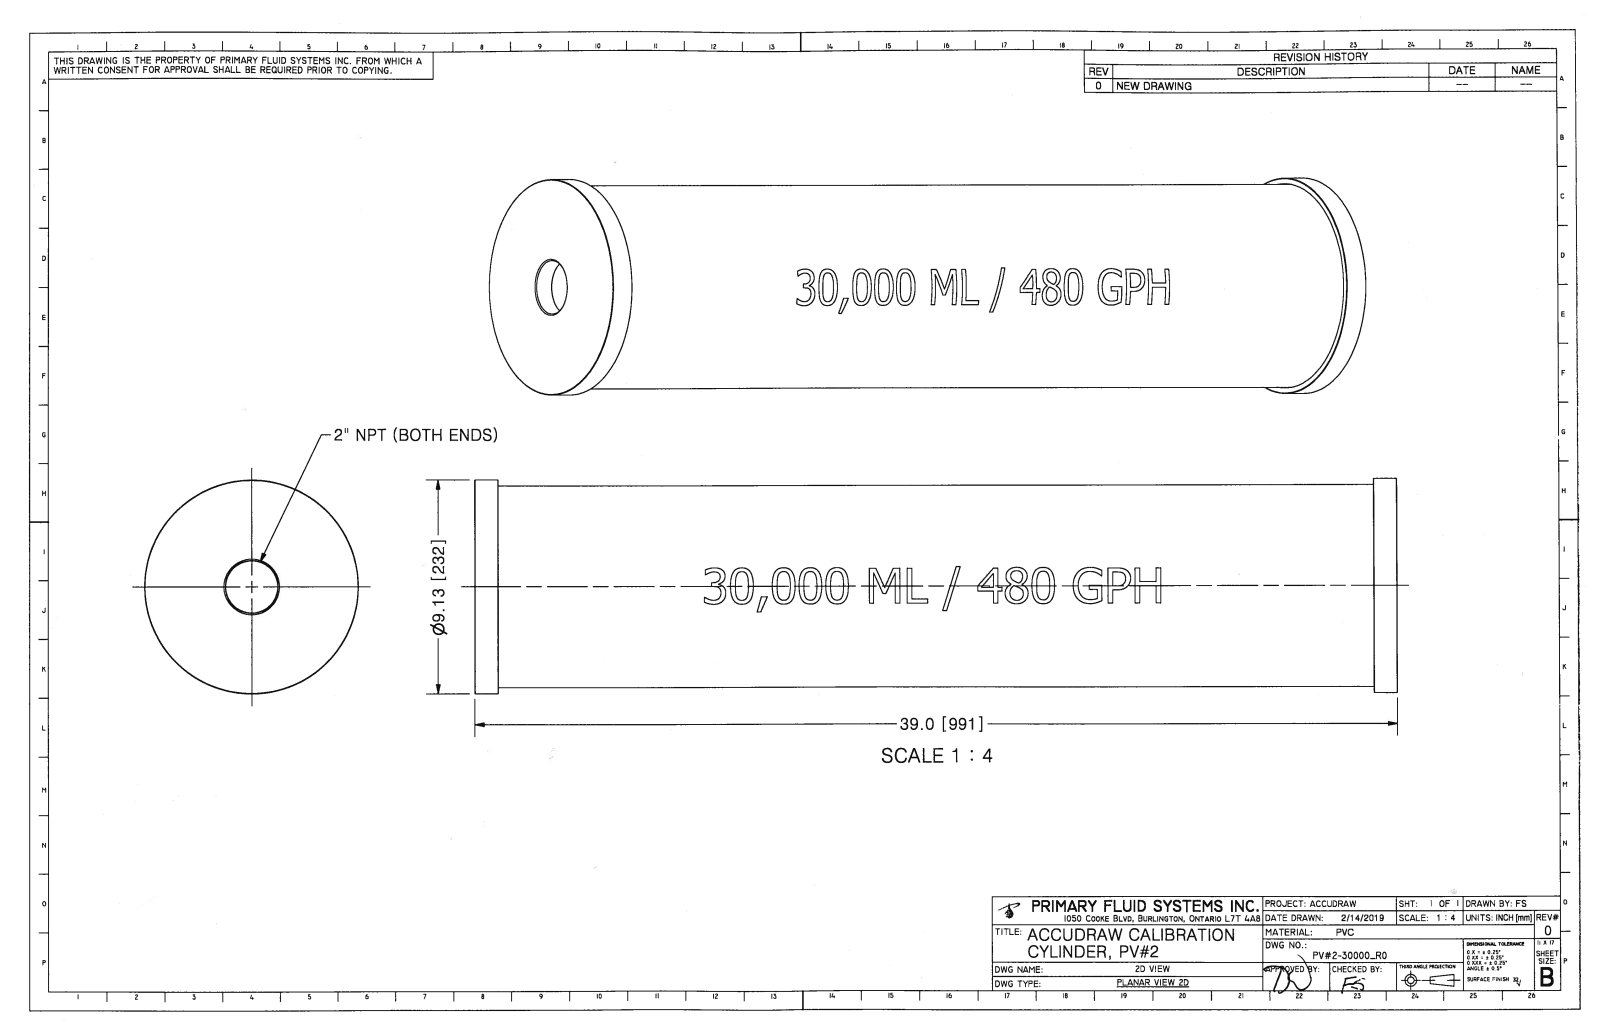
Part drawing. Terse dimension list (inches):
written by: Autodesk Inventor 2009 (AUTOMOTIVE_DESIGN)
unit: in
bodies: 1 solid, 252 faces (78 planar, 32 cylindrical, 142 other)
size: 39 × 9.125 × 9.125
volume: 284.1 in³; area: 2 369 in²
holes: 1× ⌀8.255, 1× ⌀8.654
bosses: 1× ⌀9.125, 1× ⌀8.599, 1× ⌀8.217
rounds: 1× R4.299
face distances: 39, 38, 1, 37, 0.5, 38.5, 37.5, 0.2, 9.639, 8.502
